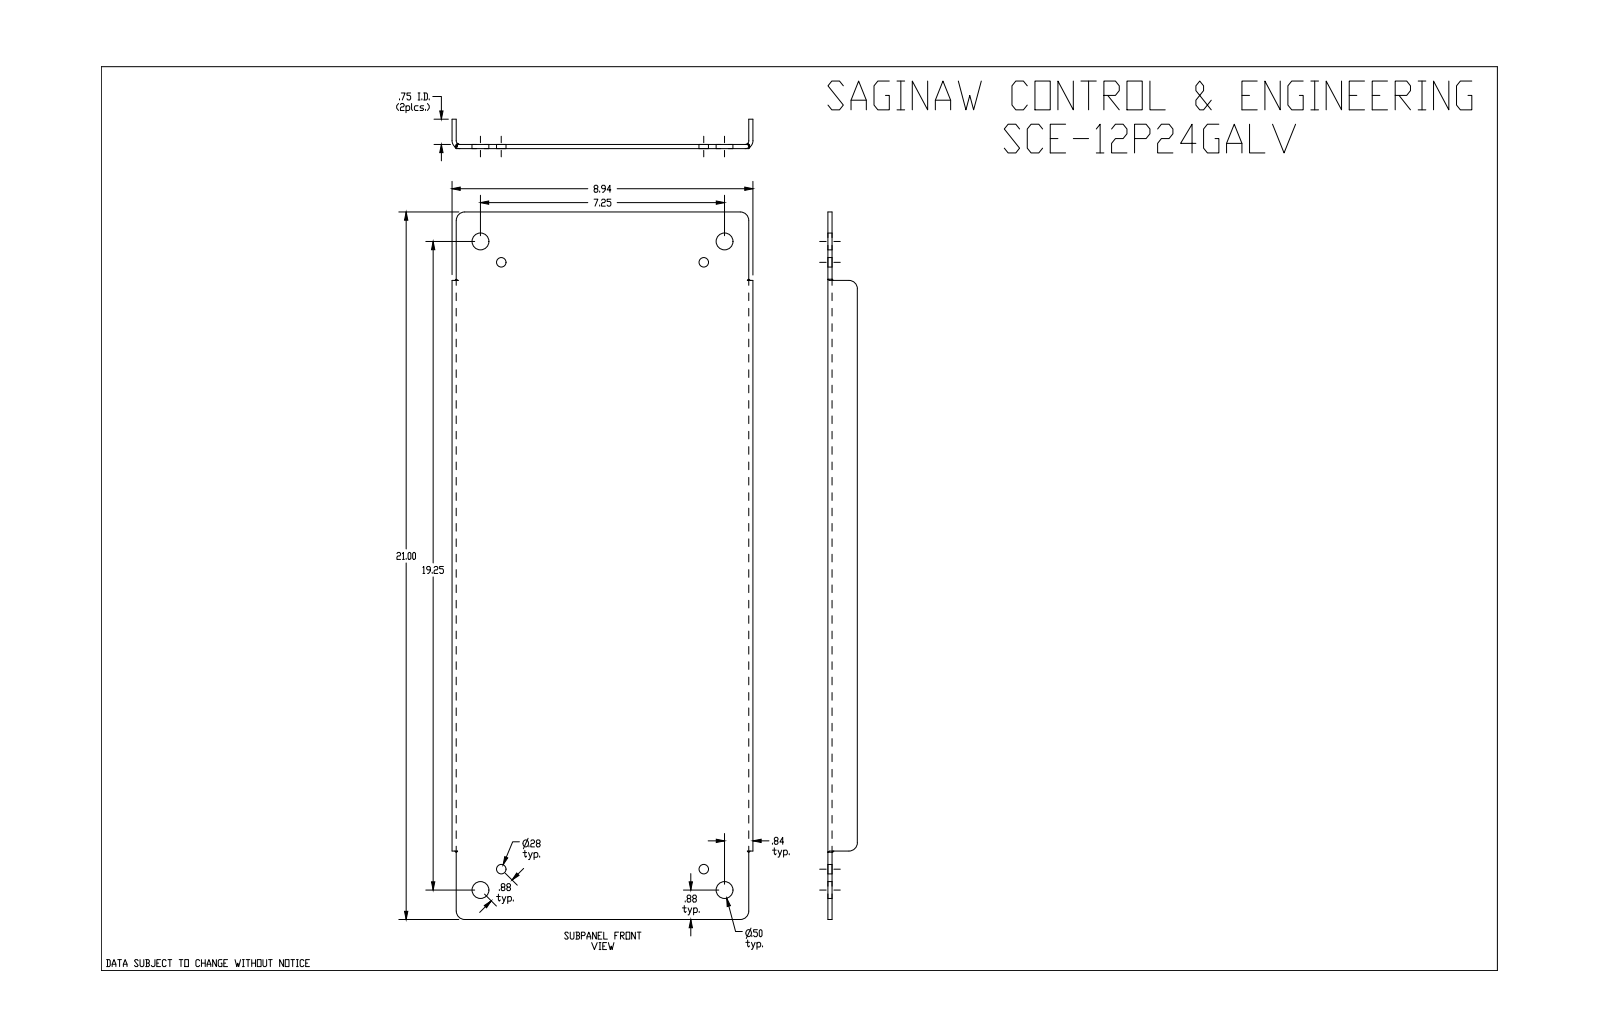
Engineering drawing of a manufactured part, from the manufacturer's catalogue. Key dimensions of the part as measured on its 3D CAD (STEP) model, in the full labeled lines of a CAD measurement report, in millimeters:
Part name (STEP PRODUCT): SCE-12P24GALV
STEP written by: SolidWorks 2019 (CONFIG_CONTROL_DESIGN)
Units: millimetres
Bodies: 1 solid, 50 faces (18 planar, 20 cylindrical, 12 other)
Overall size (bounding box): 533.4 × 227 × 22.2
Volume: 426 900 mm³ · Surface area: 274 600 mm²
Round holes (diameter × count): ⌀7.1 ×4, ⌀12.7 ×4
Partial cylindrical surfaces — rounded edges, fillets, slot ends (radius × count): R6.4 ×6, R2.8 ×2, R6 ×2
Main face-to-face distances: 3.2, 3.2, 223.9, 220.6, 227, 19.1, 22.2, 533.4, 51.6, 481.8
Hole centre spacings: 22.2, 169.2, 473.5, 502.3, 152.7, 184.2, 457.5, 482.3
